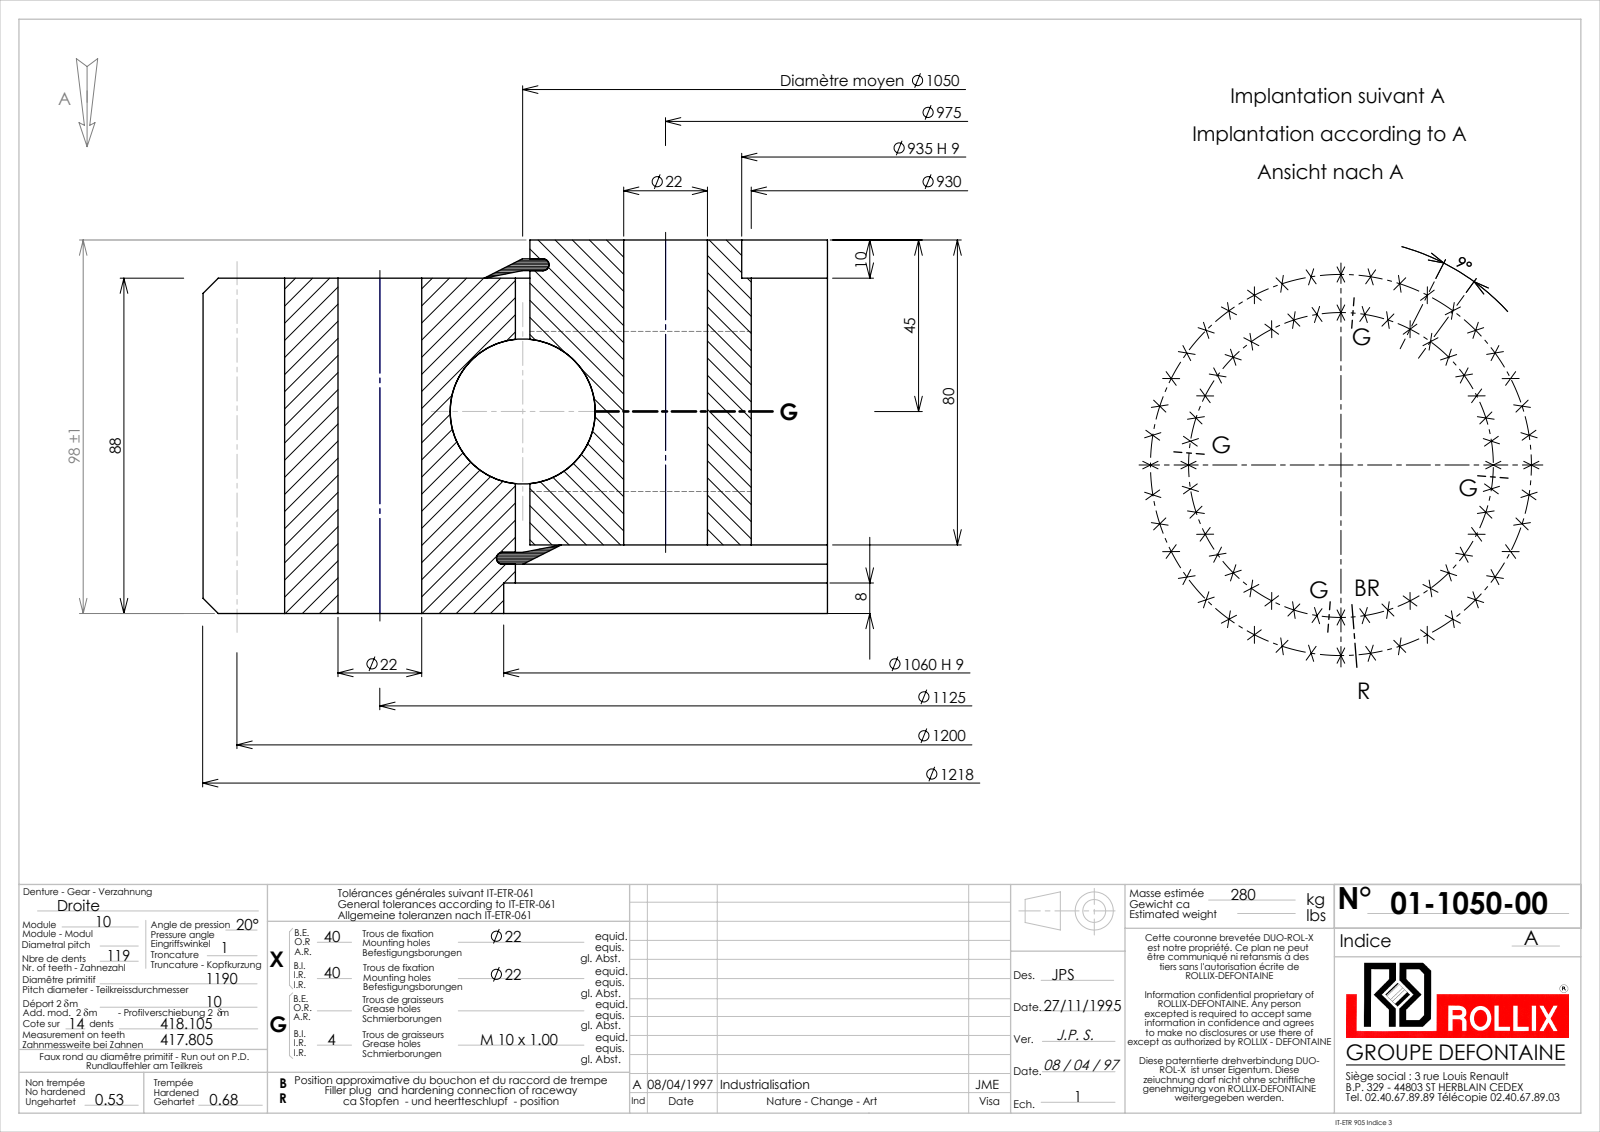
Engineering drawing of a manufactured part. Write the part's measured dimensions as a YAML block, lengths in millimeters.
part_name: "01-1050-00"
step_written_by: "SolidWorks 2016 (CONFIG_CONTROL_DESIGN)"
units: millimeters
bodies: {solids: 5, faces: 944, planar: 252, cylindrical: 425, other: 267}
overall_size: [1217.98, 1217.9, 98]
volume: 31080000
surface_area: 3136000
round_holes:
  - {diameter: 22, count: 80}
  - {diameter: 9, count: 4}
  - {diameter: 930, count: 1}
  - {diameter: 935, count: 1}
  - {diameter: 1053.81, count: 1}
  - {diameter: 1060, count: 1}
round_bosses_or_shafts:
  - {diameter: 1046.19, count: 1}
partial_cylinders:
  - {radius: 587.5, count: 1}
  - {radius: 609, count: 1}
face_to_face_distances: [88, 10, 80, 18, 70, 98, 5.05, 75.05, 1.95, 71.95]
hole_center_spacings: [510.74, 175.99, 430.52, 1002.38, 1121.53, 587.81, 88.27, 262.63]
